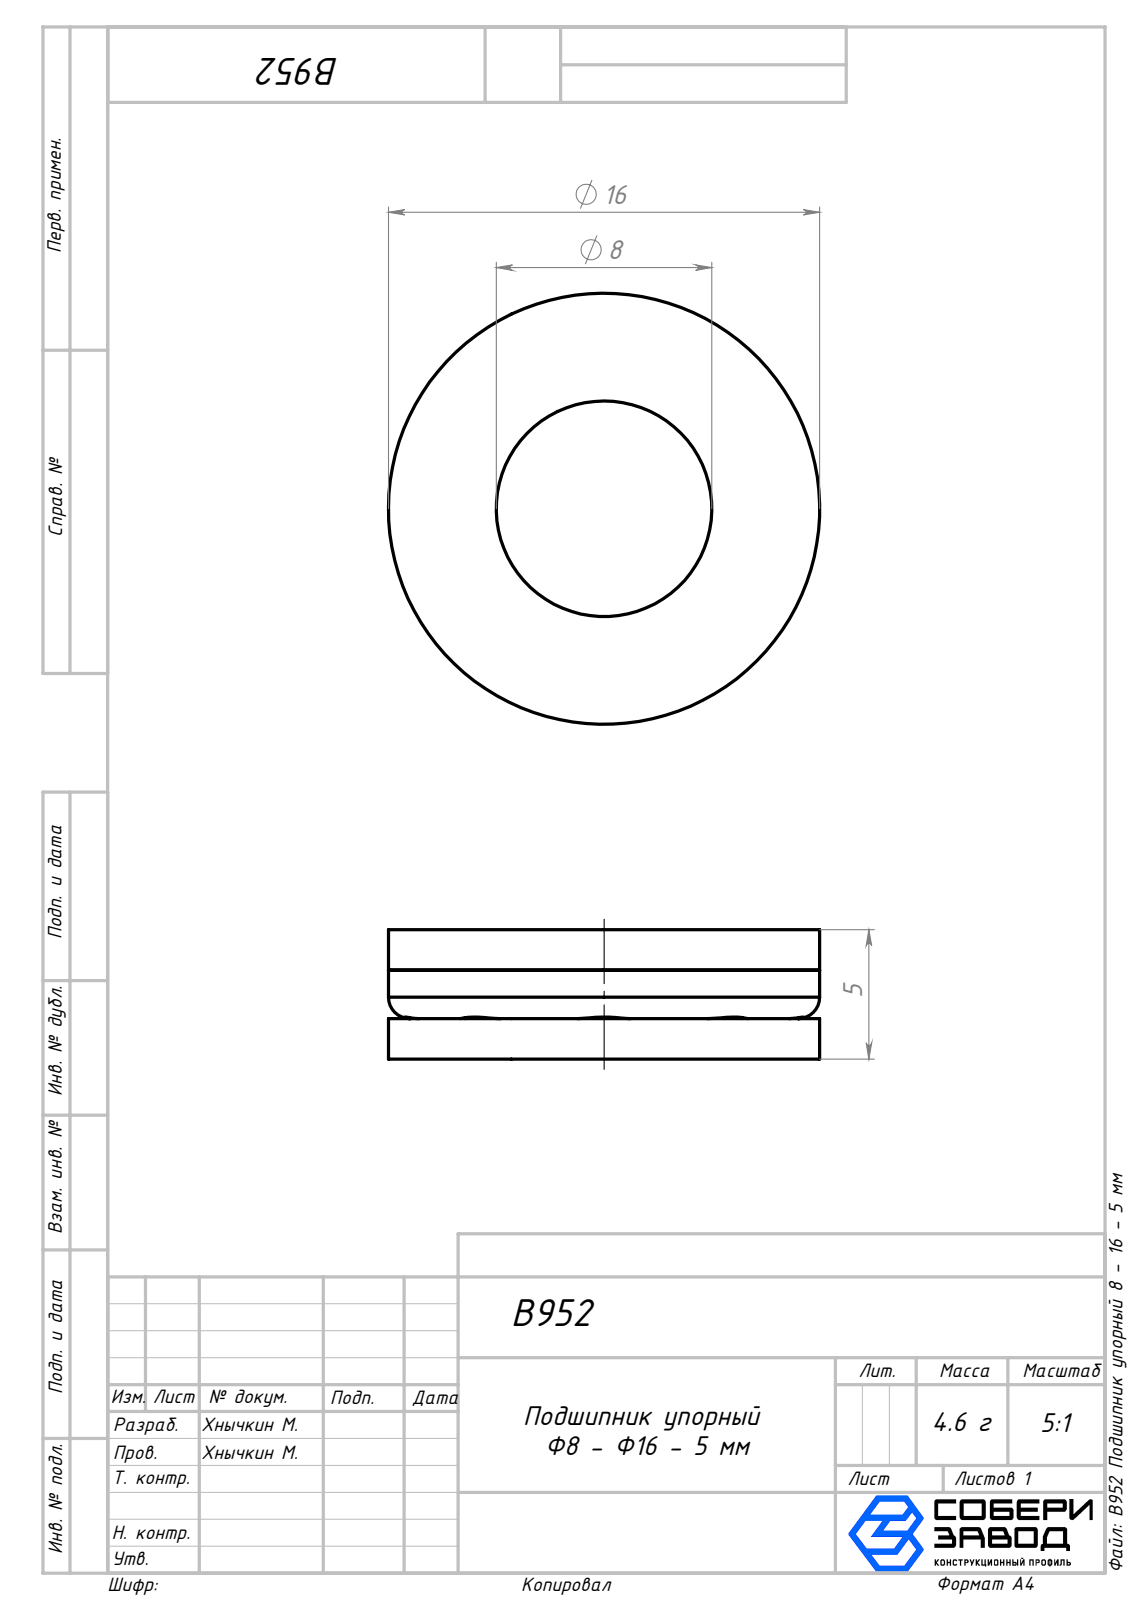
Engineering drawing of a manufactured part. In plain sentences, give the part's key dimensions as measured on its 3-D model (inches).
The part is named "B952 Первая часть_00; B992 Внутренняя часть_00; B952 Шарик_00; B952 Подшипник упорный 8 - 16 - 5 мм". Its 3-D file was written by "SolidWorks 2026 (AUTOMOTIVE_DESIGN)". It is 12 solids with 74 faces: 12 planar, 34 cylindrical and 28 other. Overall it measures 0.63 by 0.63 by 0.189 inches. Its volume is 0.035 cubic inches and its surface area 2.443 square inches. Round holes: 9 of diameter 0.118, 1 of diameter 0.315, 1 of diameter 0.614. Round bosses or shafts: 1 of diameter 0.63, 1 of diameter 0.331. The main face-to-face distances are 0.059, 0.13, 0.189, 0.094, 0.035, 0.071, 0.033, 0.156, 0.026, 0.061. The hole center spacings are 0.236, 0.304, 0.465, 0.162, 0.409, 0.409, 0.161, 0.466.
